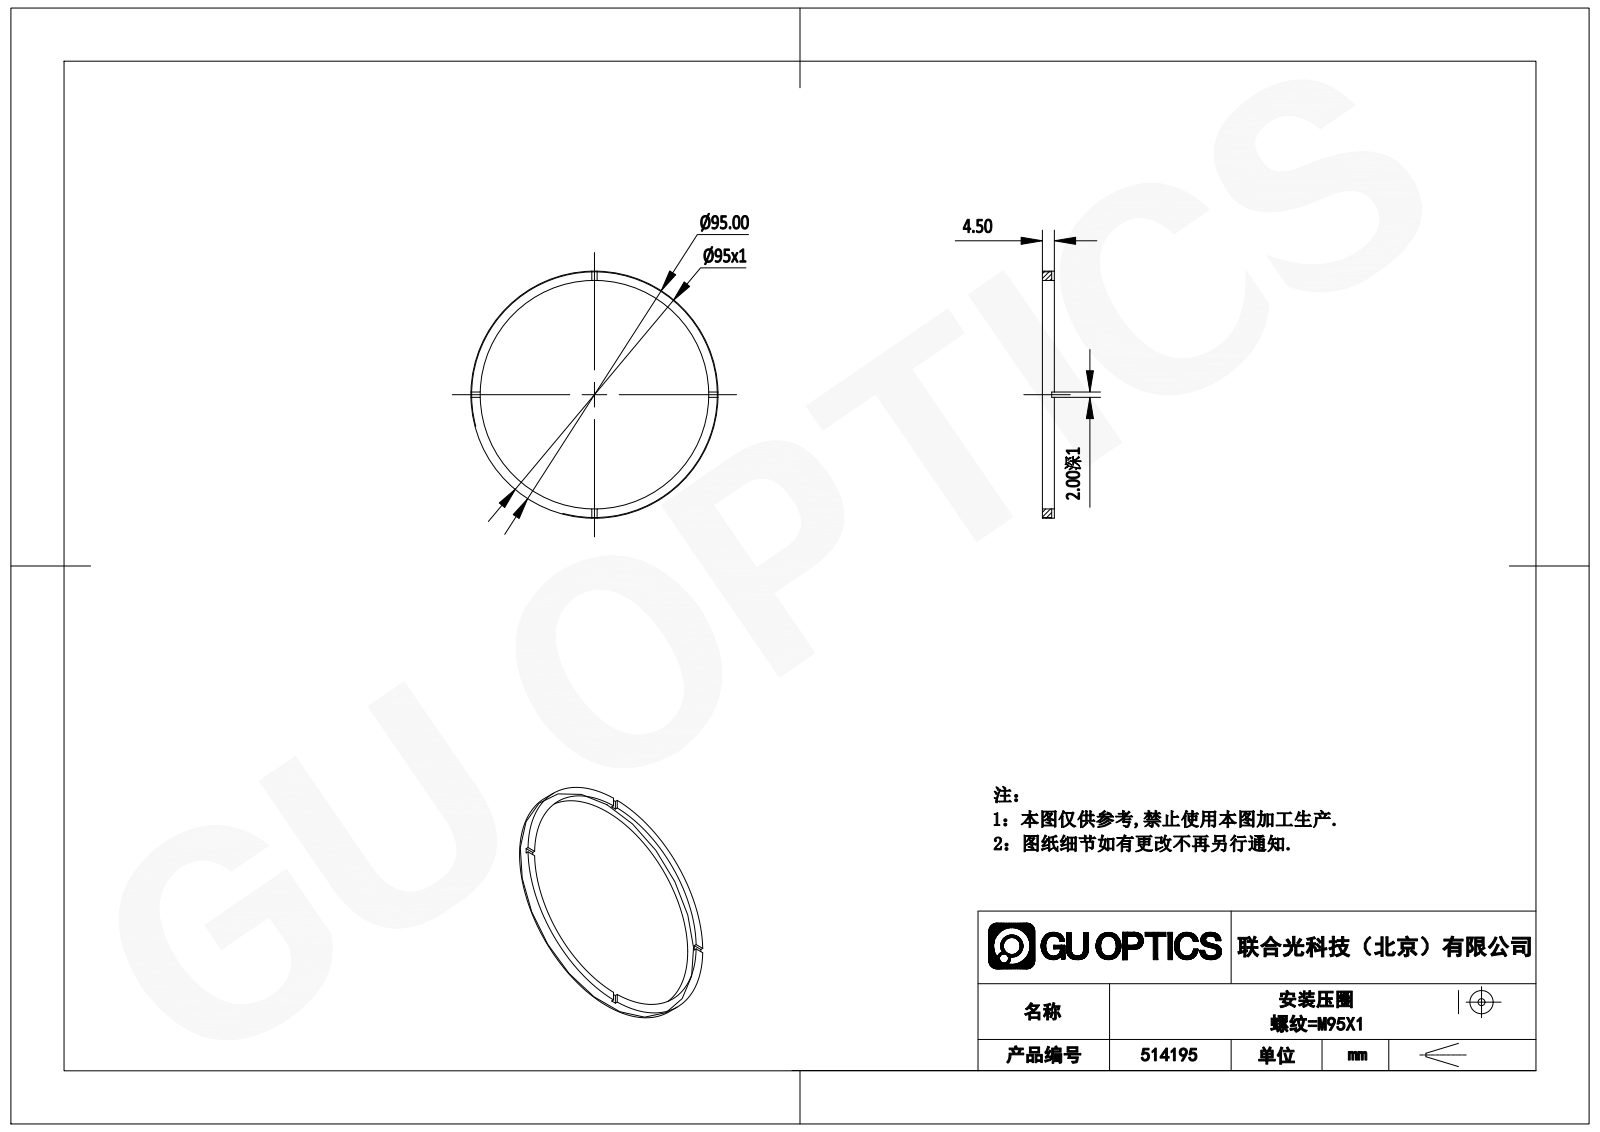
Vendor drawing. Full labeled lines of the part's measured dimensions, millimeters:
Part name (STEP PRODUCT): 514195
STEP written by: SolidWorks 2020 (CONFIG_CONTROL_DESIGN)
Units: millimetres
Bodies: 1 solid, 21 faces (17 planar, 4 cylindrical, 0 other)
Overall size (bounding box): 95 × 95 × 4.5
Volume: 4 499 mm³ · Surface area: 4 611 mm²
Round holes (diameter × count): ⌀88 ×1
Round bosses / shafts (diameter × count): ⌀95 ×1
Main face-to-face distances: 4.5, 3.5, 1, 2
